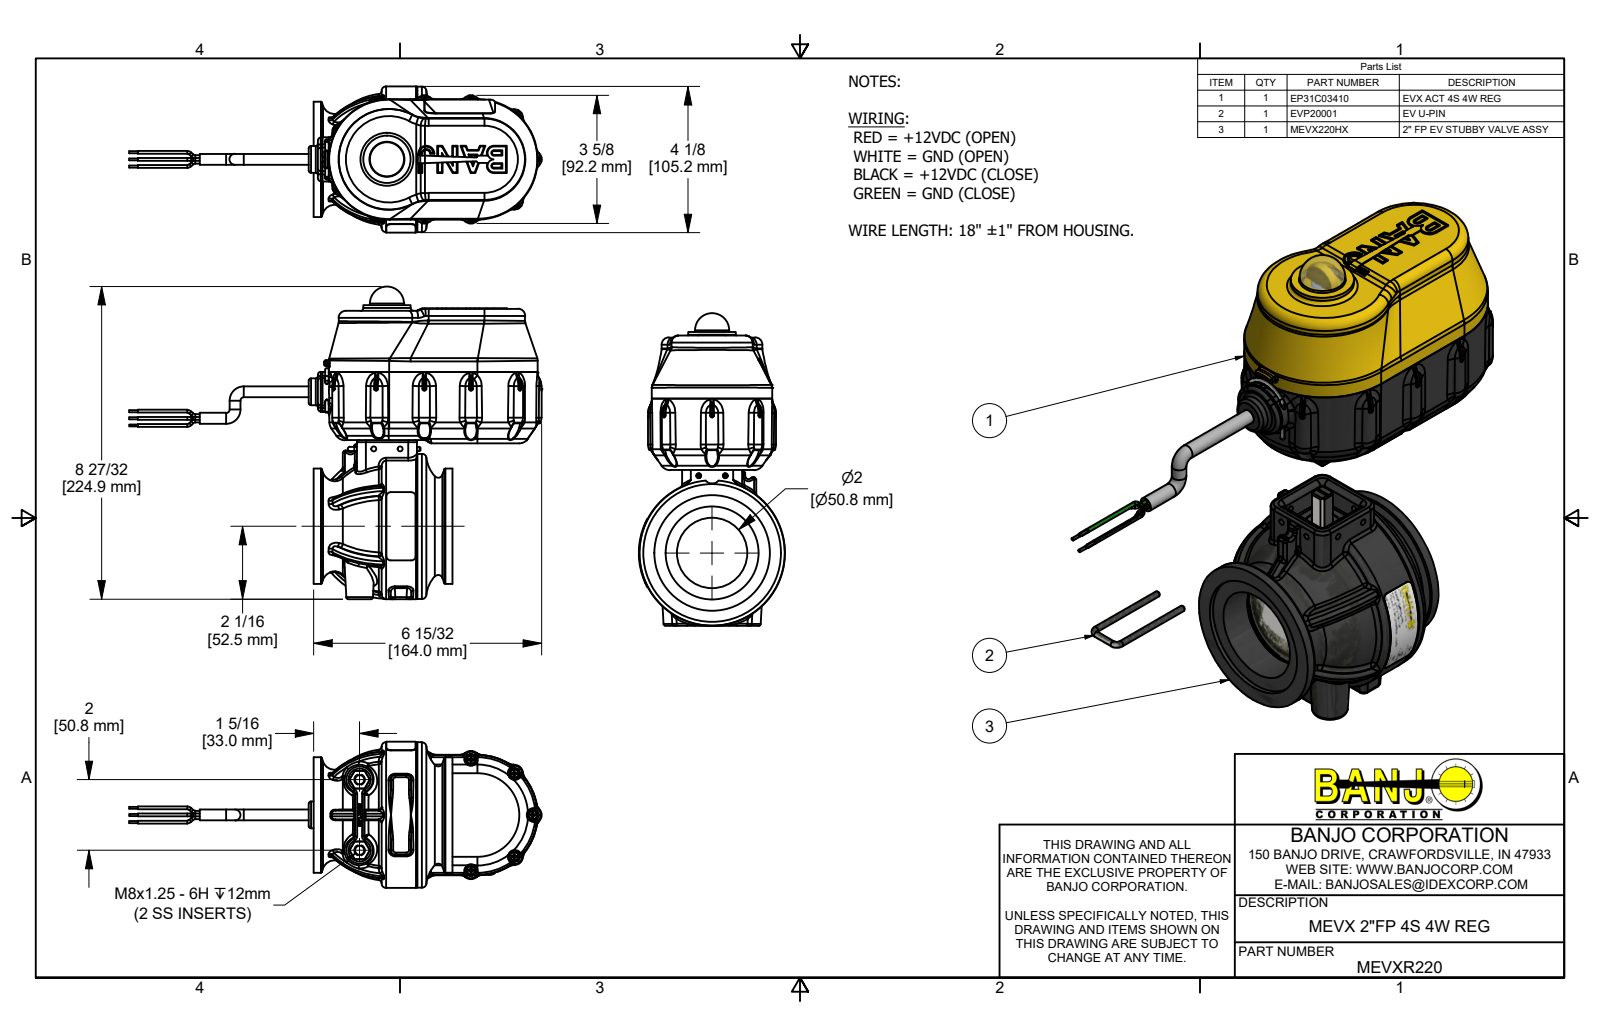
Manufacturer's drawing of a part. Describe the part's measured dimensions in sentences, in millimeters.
The part is named "MEVXR220; EP31C03410; 91400A119; 95584A200 (+8 more)". Its 3-D file was written by "Autodesk Inventor 2019 (AUTOMOTIVE_DESIGN)". It is 83 solids with 12050 faces: 3507 planar, 3056 cylindrical and 5487 other. Overall it measures 296.8 by 224.9 by 105.2 millimeters. Its volume is 886 900 cubic millimeters and its surface area 382 600 square millimeters. Round holes: 13 of diameter 3.8, 11 of diameter 2.4, 5 of diameter 3.4, 4 of diameter 2.7, 4 of diameter 3.2, 4 of diameter 3.5, 4 of diameter 4.3, 2 of diameter 2.3, 2 of diameter 2.7, 2 of diameter 2.9, 2 of diameter 3, 2 of diameter 3.1. Round bosses or shafts: 20 of diameter 2, 17 of diameter 6.4, 11 of diameter 3.6, 11 of diameter 2.7, 11 of diameter 2.2, 8 of diameter 1.5, 4 of diameter 6.9, 4 of diameter 5.6. Partial cylindrical surfaces (rounded edges, fillets, slot ends): 147 of radius 1, 83 of radius 0.5, 56 of radius 0.3, 43 of radius 0.1, 35 of radius 1.5, 30 of radius 0.8, 28 of radius 2, 25 of radius 3.2. The main face-to-face distances are 2.5, 65.2, 42.8, 19.8, 62.6, 22.4, 0.9, 25.1, 76.3, 1.4. The hole center spacings are 56.4, 32.6, 42.2, 69.3, 75.4, 87.6, 12.4, 12.5.
